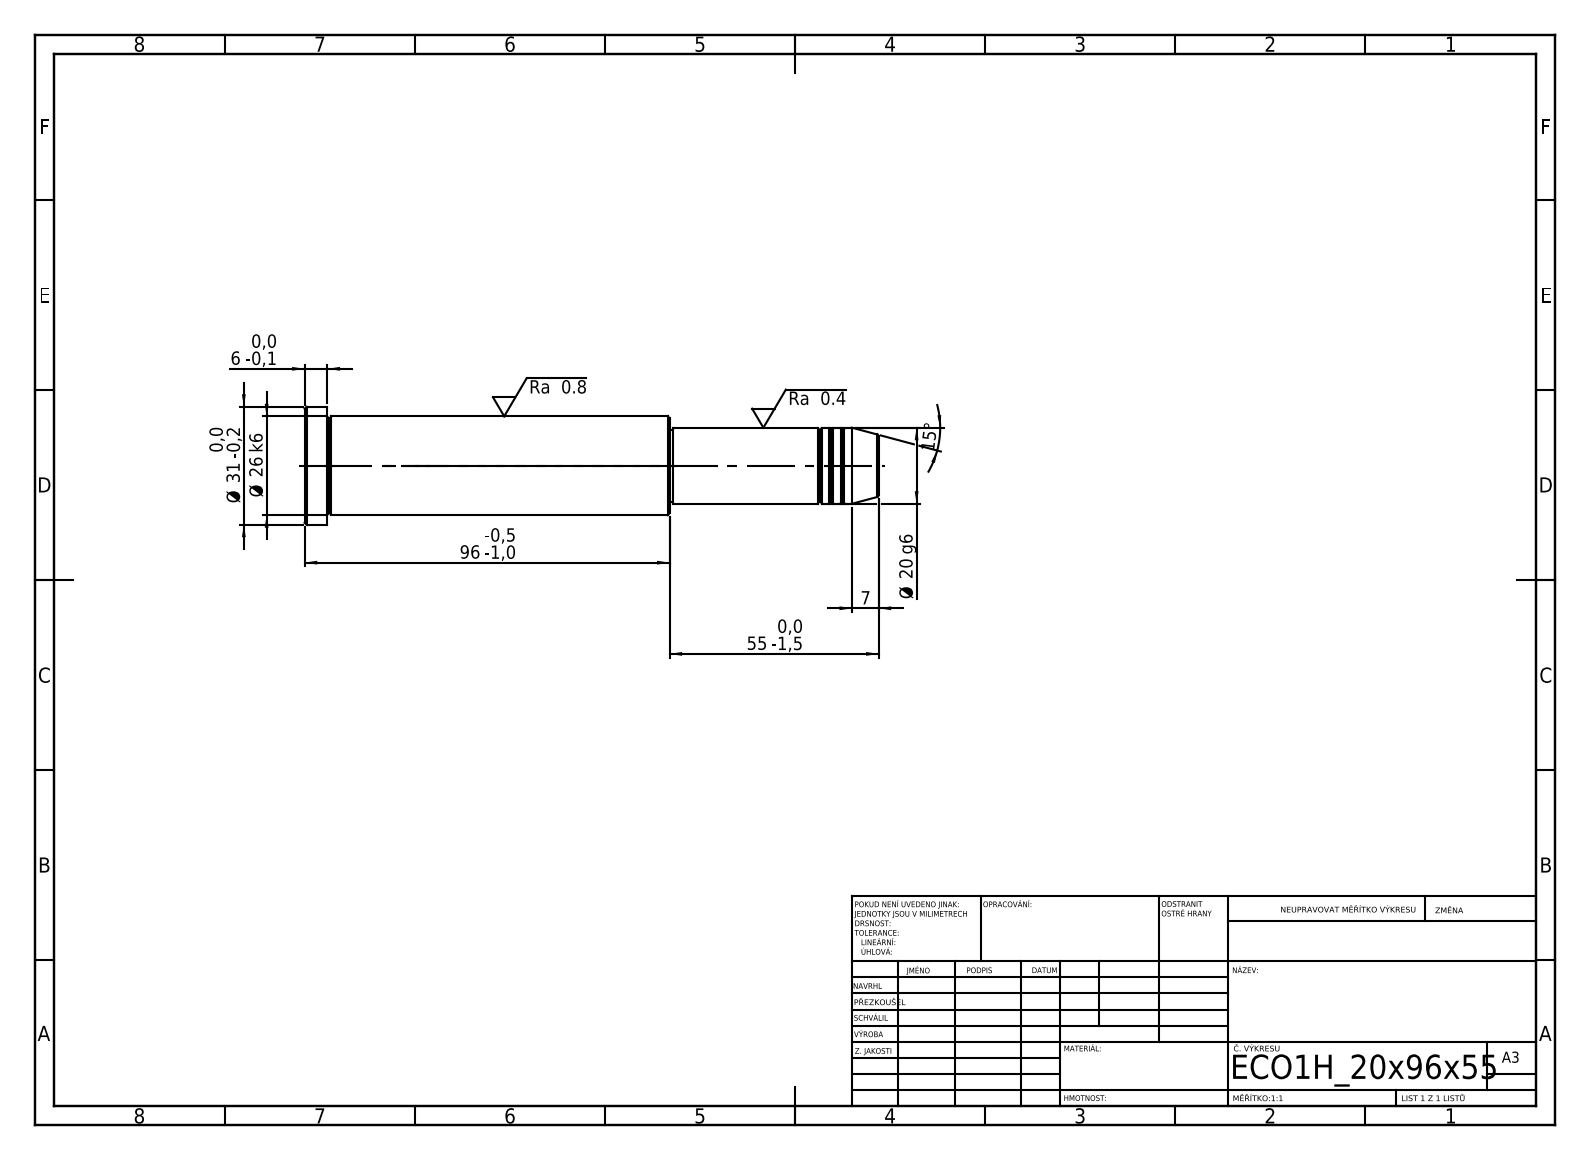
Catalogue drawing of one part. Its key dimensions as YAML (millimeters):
step_written_by: "SolidWorks 2019 (CONFIG_CONTROL_DESIGN)"
units: millimeters
bodies: {solids: 1, faces: 43, planar: 5, cylindrical: 14, other: 24}
overall_size: [151, 31, 31]
volume: 69046
surface_area: 12908
round_bosses_or_shafts:
  - {diameter: 31, count: 1}
  - {diameter: 26, count: 1}
  - {diameter: 20, count: 1}
  - {diameter: 19, count: 1}
face_to_face_distances: [6, 90, 96, 55, 145, 151, 54, 1, 91, 97]
